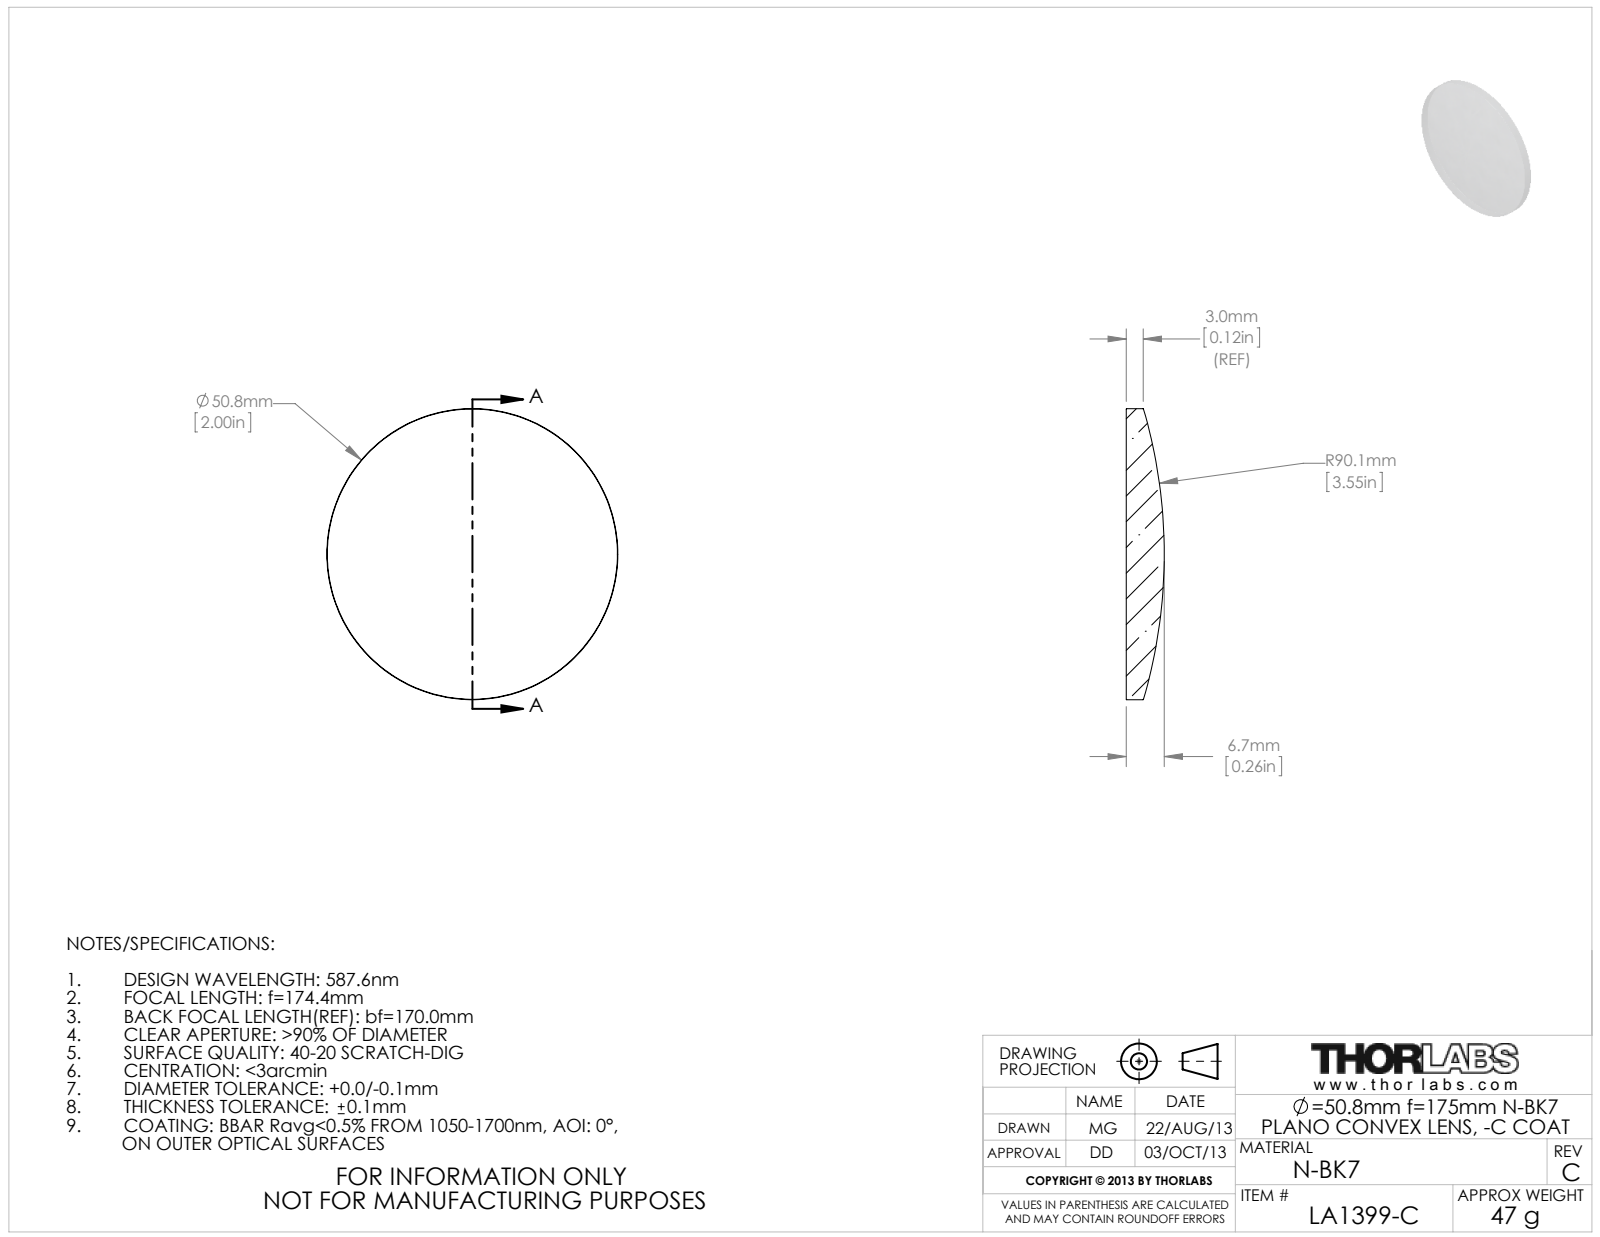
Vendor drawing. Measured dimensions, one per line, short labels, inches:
name: 4605-E0W
written by: SolidWorks 2009 (AUTOMOTIVE_DESIGN)
unit: in
bodies: 0 solids, 5 faces (1 planar, 2 cylindrical, 2 other)
size: 2 × 2 × 0.262
bosses: 1× ⌀2
